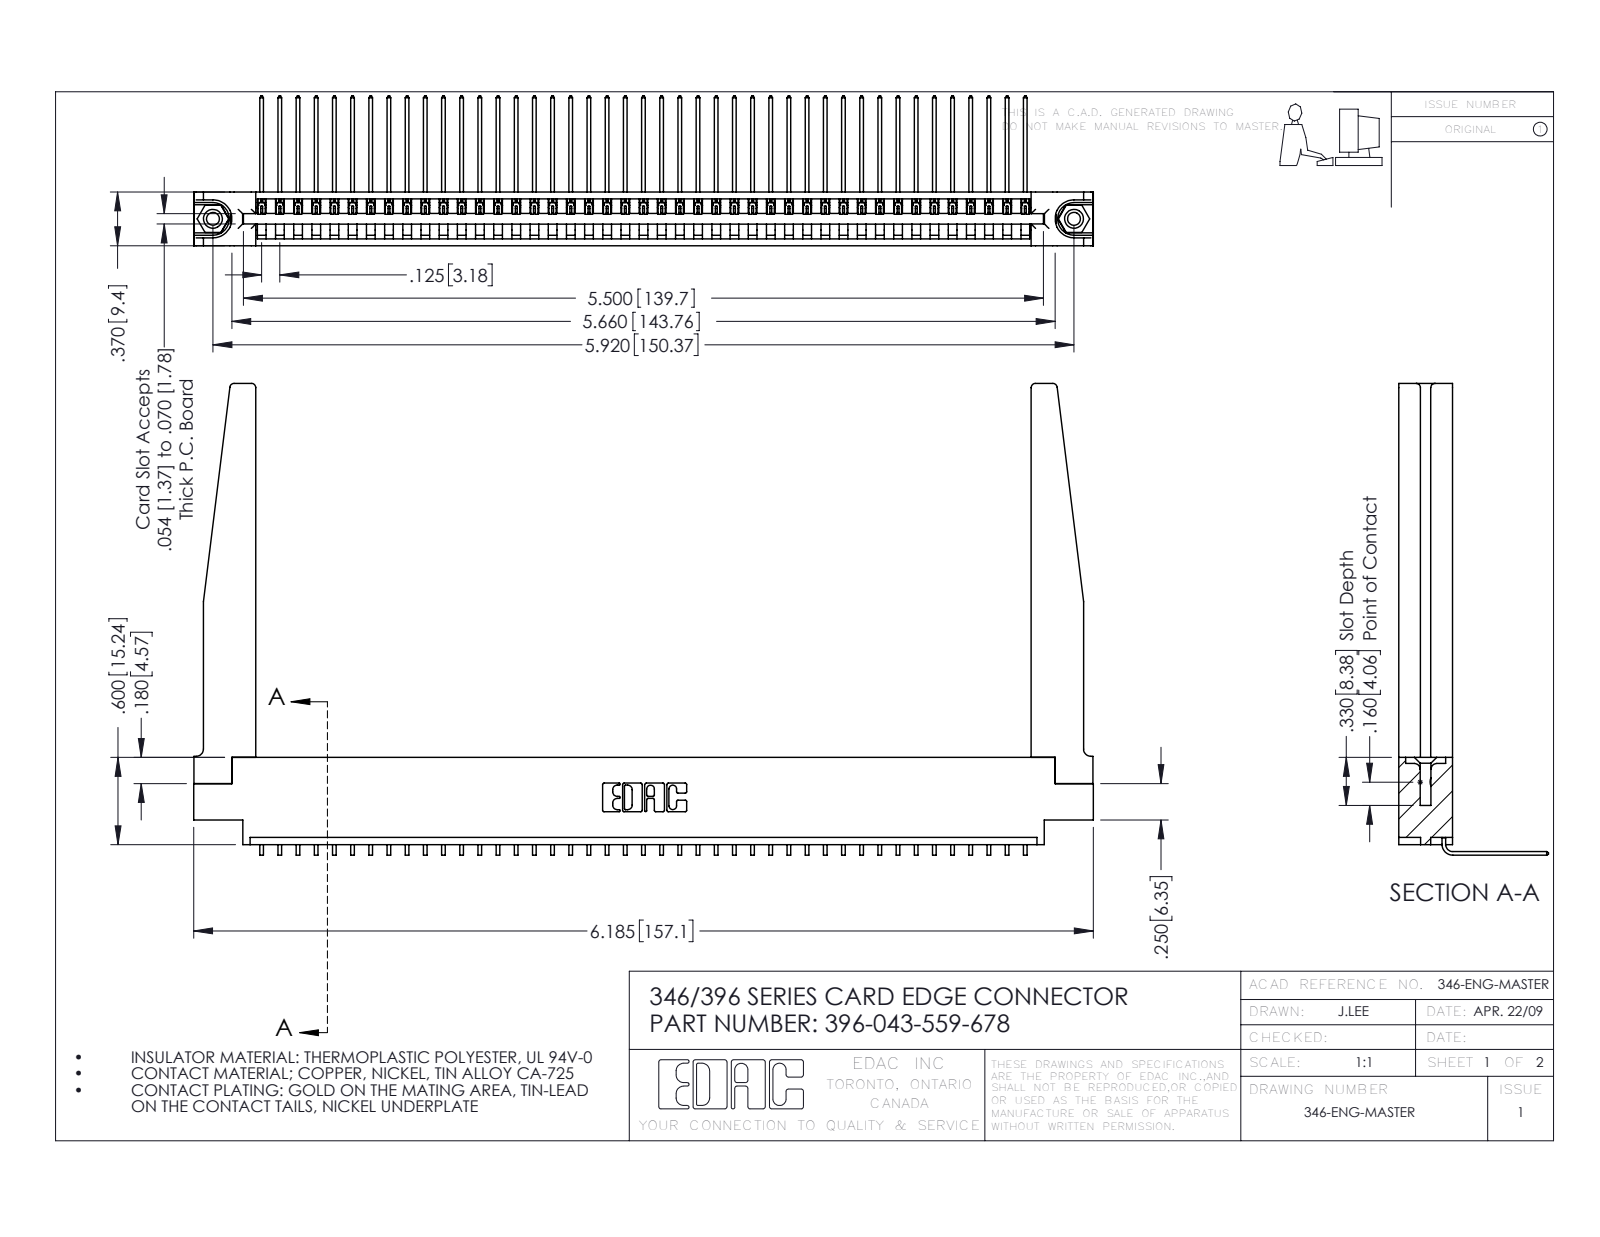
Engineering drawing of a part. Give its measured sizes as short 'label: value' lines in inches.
name: 396-043-559-678; 346-220-078_345-220-078; 346 Part_0.170 Offset - 0.156 Dia-TH; 345-250-001_345-250-001-102 (+1 more)
written by: SolidWorks 2016 (CONFIG_CONTROL_DESIGN)
unit: in
bodies: 48 solids, 2940 faces (2028 planar, 860 cylindrical, 52 other)
size: 6.185 × 3.243 × 1.03
volume: 1.339 in³; area: 40.85 in²
holes: 2× ⌀0.089, 2× ⌀0.125, 2× ⌀0.156, 1× ⌀0.064
bosses: 2× ⌀0.155
rounds: 86× R0.006, 22× R0.01, 8× R0.03, 6× R0.007, 6× R0.031, 3× R0.026, 3× R0.05, 2× R0.031
face distances: 0.37, 0.048, 0.322, 0.072, 0.148, 0.15, 0.025, 0.25, 0.298, 0.222
hole spacings: 0.246, 5.711, 5.92
